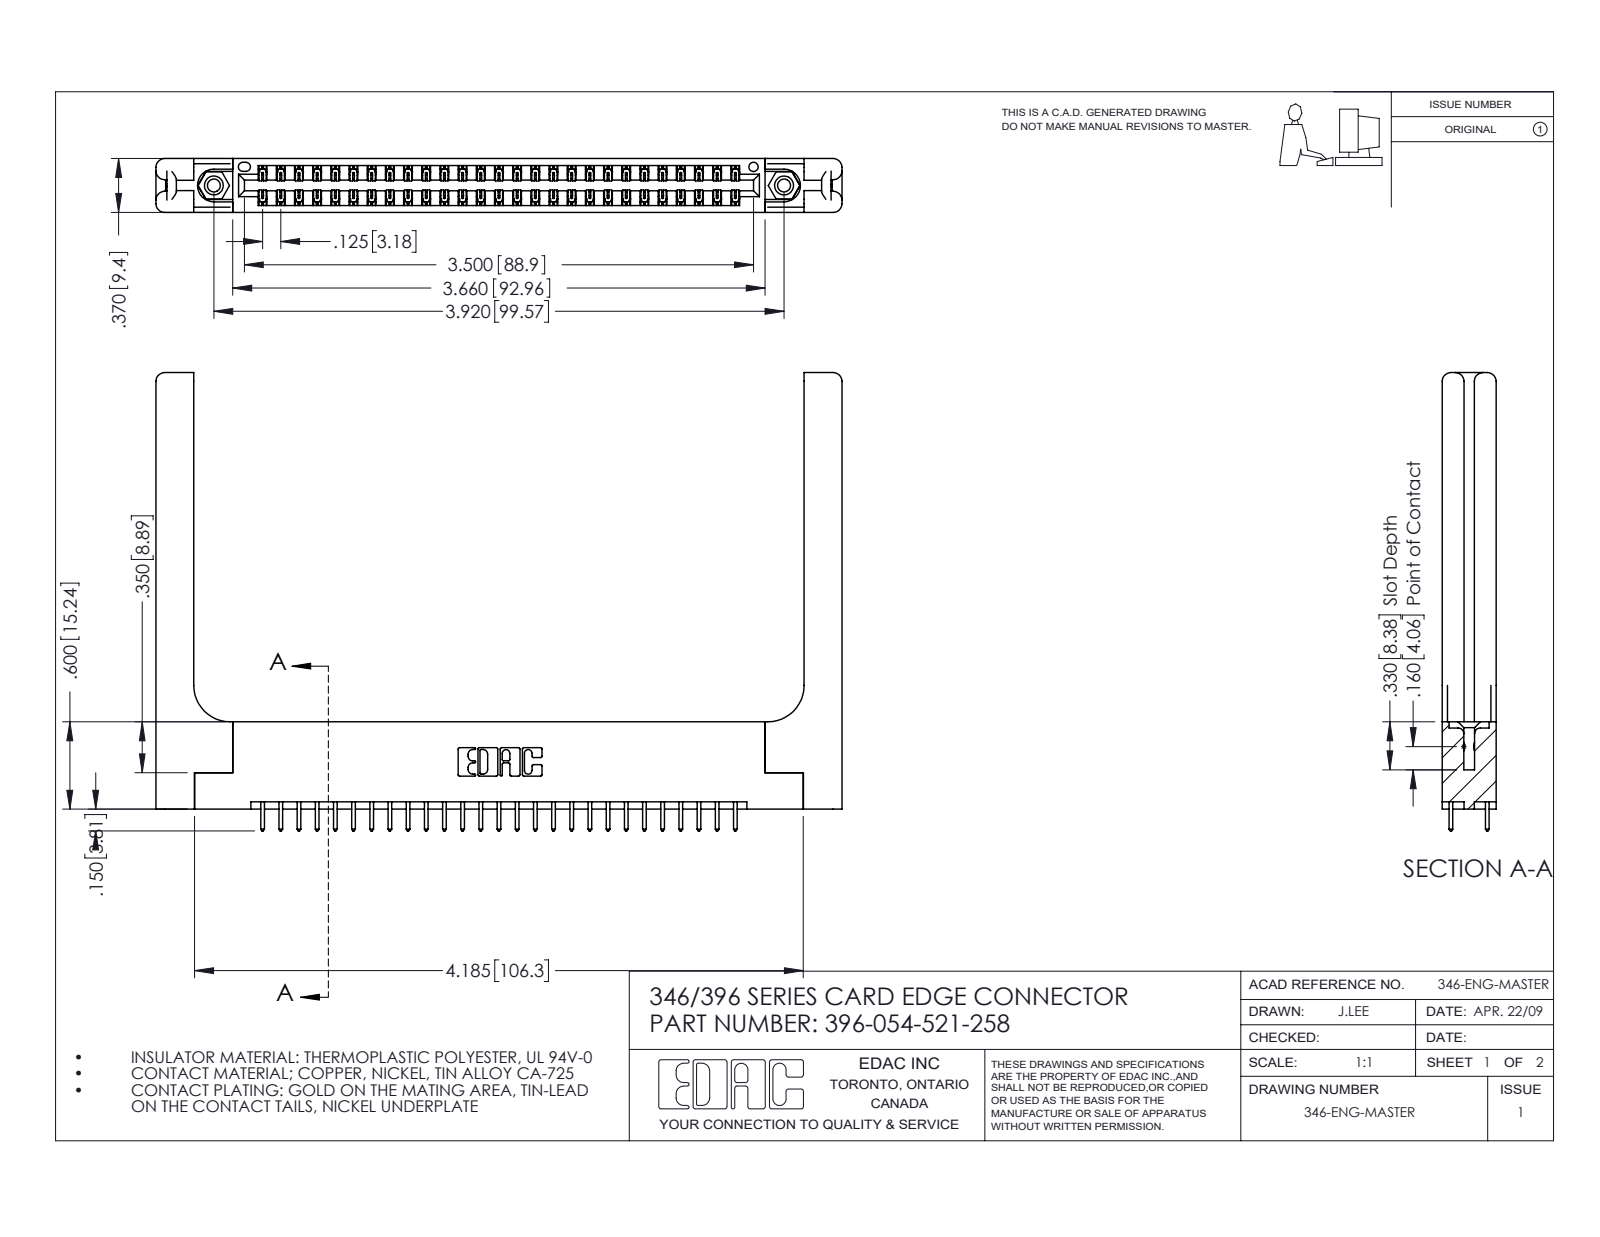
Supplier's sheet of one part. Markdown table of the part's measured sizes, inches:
| quantity | value |
| --- | --- |
| part name | 346-220-058_345-220-058; 346 Part_Flush Mounting Lugs - 0.156 Dia-TH; 345-292-001_345-293-121; 396-054-521-258 (+1 more) |
| STEP written by | SolidWorks 2016 (CONFIG_CONTROL_DESIGN) |
| units | inches |
| bodies | 59 solids, 3186 faces (2114 planar, 1012 cylindrical, 60 other) |
| overall size | 4.716 × 3.15 × 0.37 |
| volume | 1.162 in³ |
| surface area | 31.7 in² |
| round holes (diameter × count) | 0.089 × 2, 0.125 × 2, 0.156 × 2, 0.064 × 1 |
| round bosses / shafts (diameter × count) | 0.155 × 2 |
| partial cylindrical surfaces (radius × count) | 0.006 × 81, 0.01 × 54, 0.01 × 22, 0.06 × 16, 0.007 × 6, 0.031 × 6, 0.026 × 3, 0.014 × 2 |
| main face-to-face distances | 0.37, 0.072, 0.048, 0.322, 0.148, 0.15, 0.25, 0.025, 0.298, 0.275 |
| hole center spacings | 0.246, 3.712, 3.92 |
